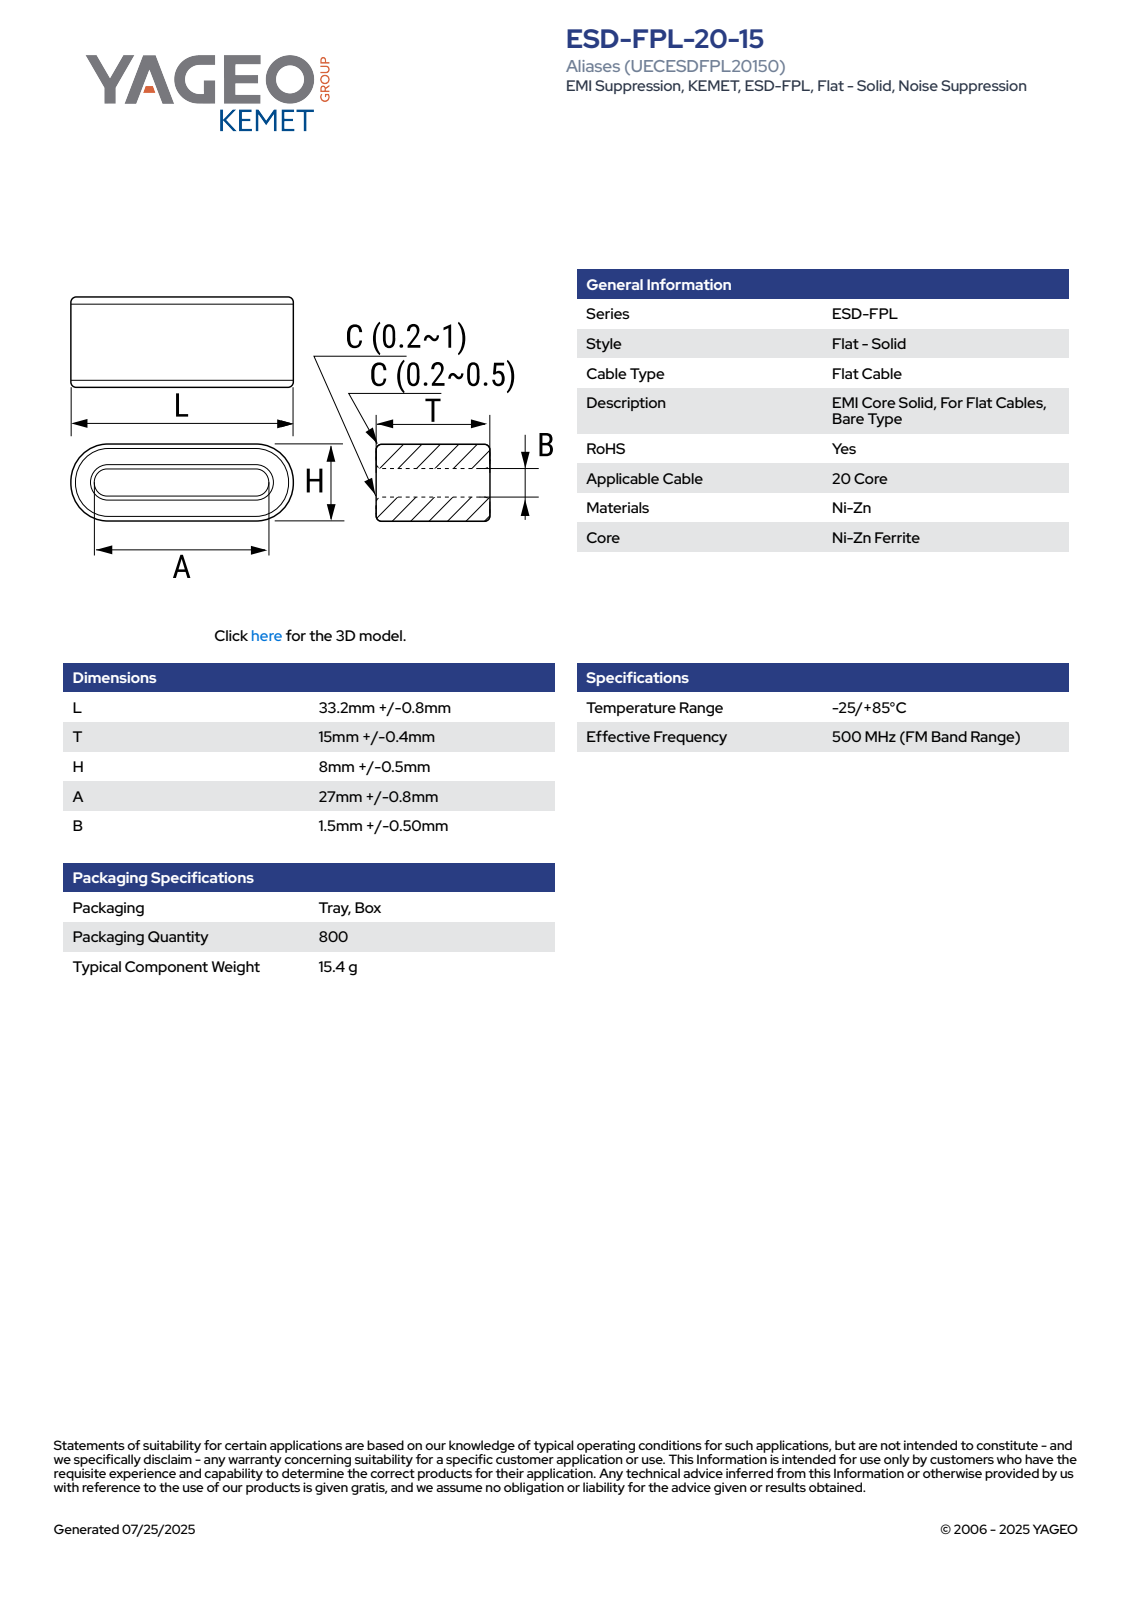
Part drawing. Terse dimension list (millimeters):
name: EC_FPL3_L34T15.4H8.5A27B1.5
written by: SolidWorks 2021 (AUTOMOTIVE_DESIGN)
unit: mm
bodies: 4 solids, 95 faces (63 planar, 16 cylindrical, 16 other)
size: 34 × 15.4 × 8.5
volume: 3 593 mm³; area: 2 523 mm²
rounds: 8× R0.2, 2× R0.75, 2× R4.25
face distances: 3.5, 5, 1.5, 8.5, 15.4, 6.69, 8.71, 2.02, 0.5, 7.08
